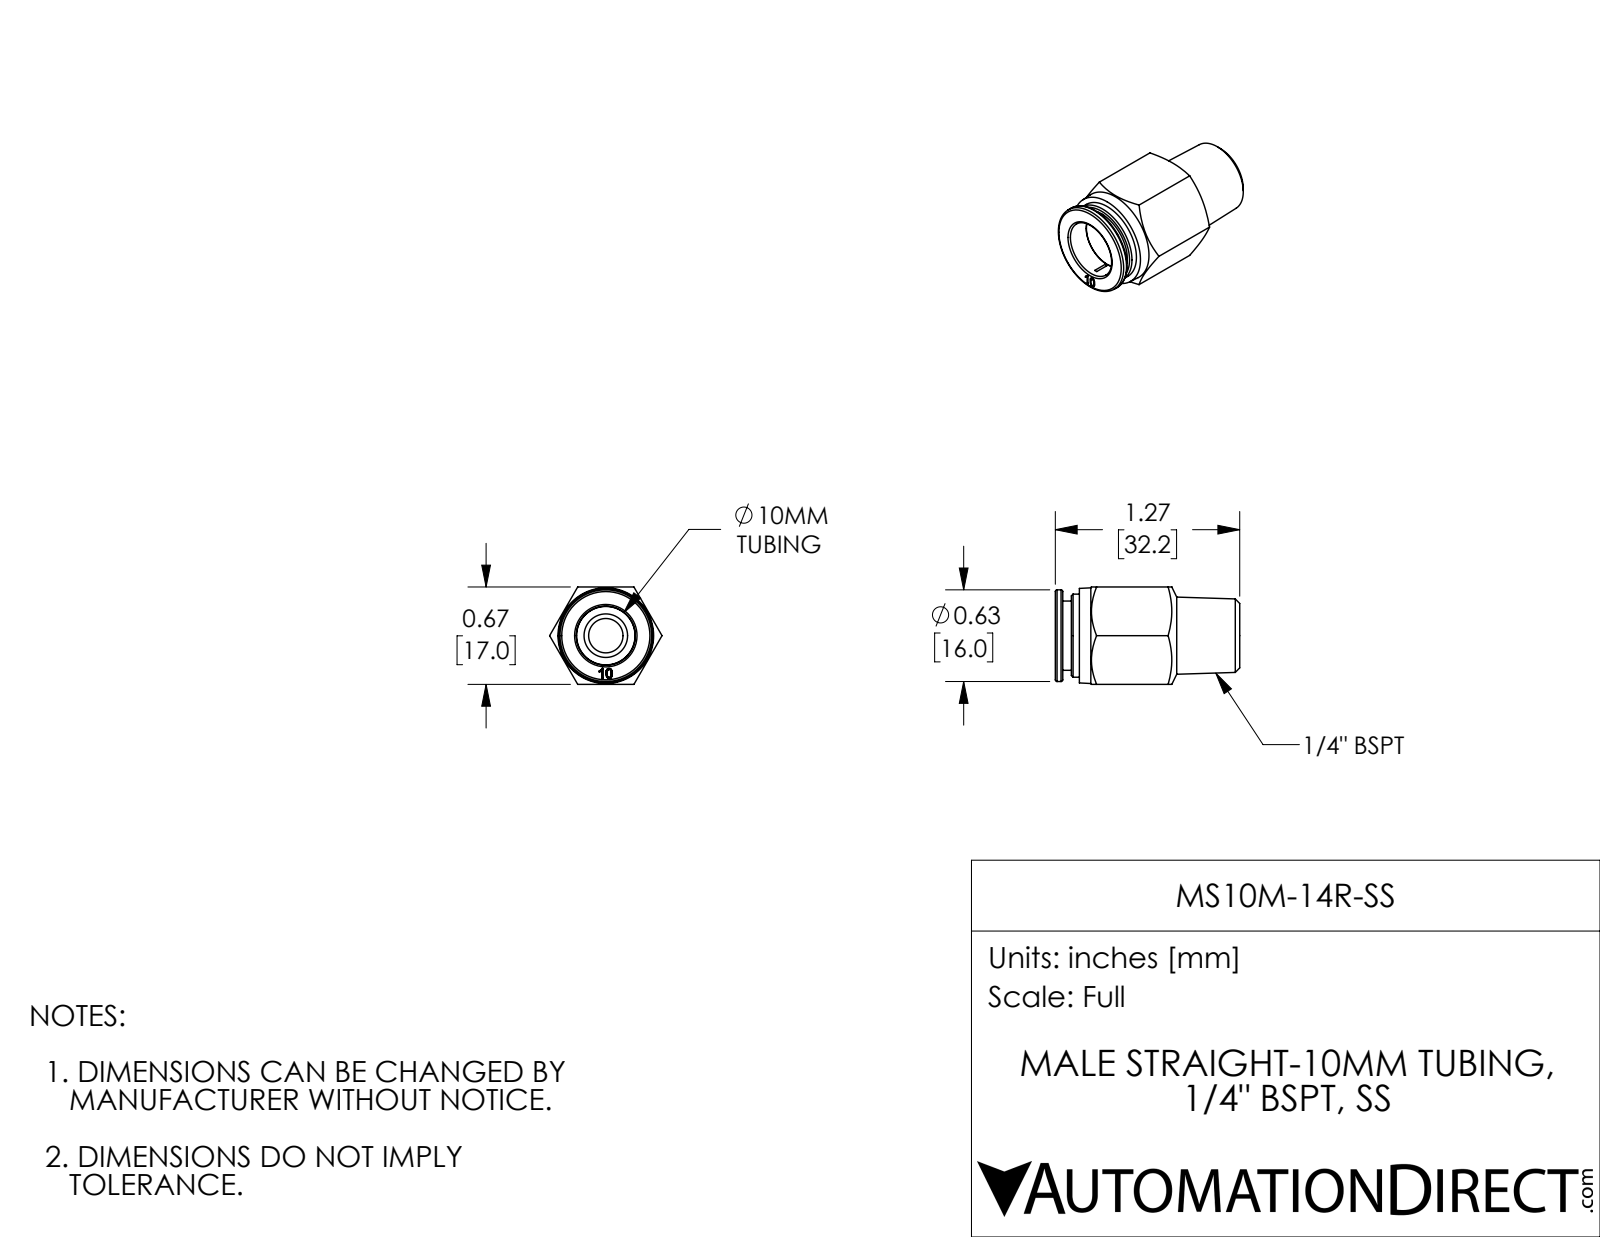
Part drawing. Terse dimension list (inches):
name: MS10M-14R-SS
written by: SolidWorks 2017 (AUTOMOTIVE_DESIGN)
unit: in
bodies: 1 solid, 78 faces (27 planar, 12 cylindrical, 39 other)
size: 1.268 × 0.773 × 0.669
volume: 0.26 in³; area: 4.767 in²
holes: 1× ⌀0.236, 1× ⌀0.402, 1× ⌀0.406
bosses: 1× ⌀0.63, 1× ⌀0.571, 1× ⌀0.476
face distances: 0.669, 0.051, 1.217, 1.268, 1.102, 0.114, 0.165, 0.488, 0.614, 0.728
